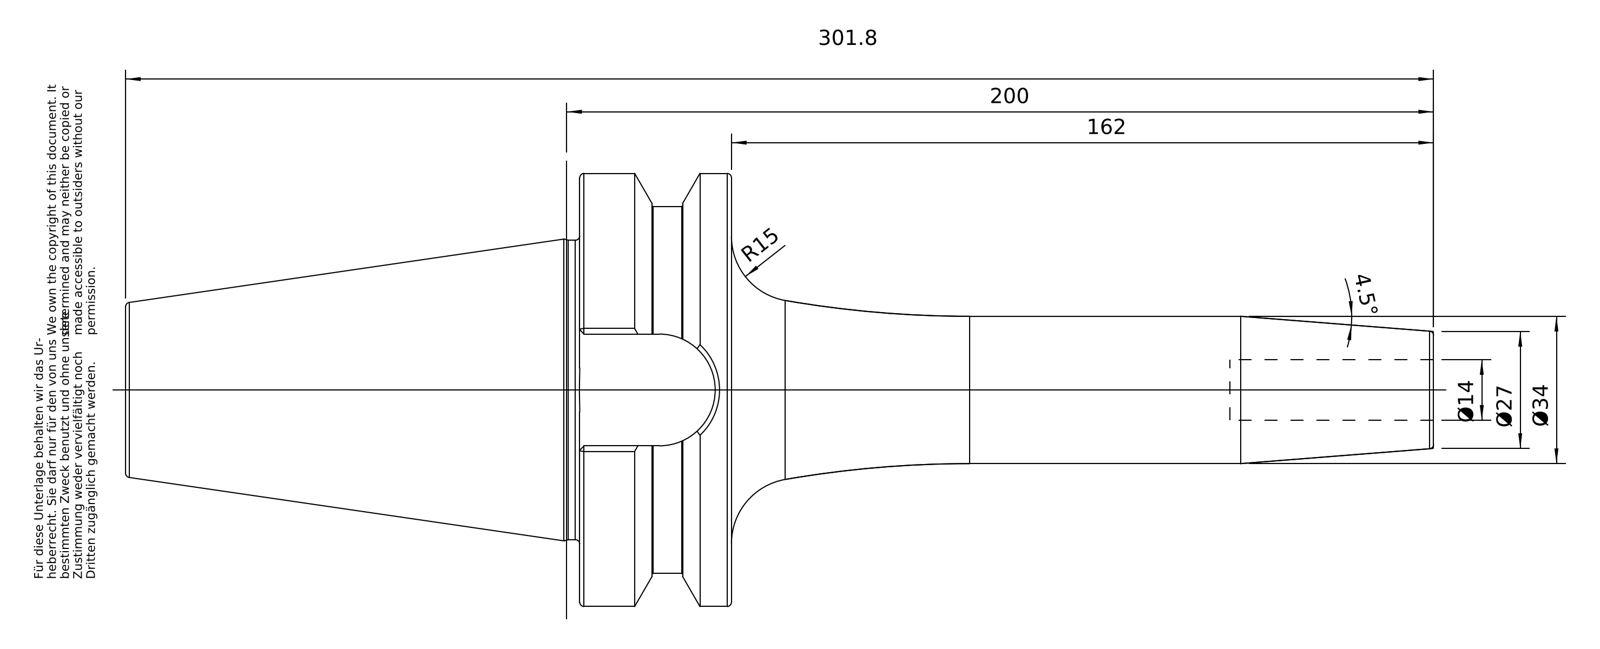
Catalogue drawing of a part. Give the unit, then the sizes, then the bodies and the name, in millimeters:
Units: millimetres
Overall size (bounding box): 301.8 × 99.97 × 99.97
Round holes (diameter × count): ⌀14 ×1, ⌀20.75 ×1, ⌀25.02 ×1, ⌀25.7 ×1
Round bosses / shafts (diameter × count): ⌀99.97 ×1, ⌀84.75 ×1, ⌀69.15 ×1, ⌀34 ×1, ⌀24.01 ×1
Partial cylindrical surfaces — rounded edges, fillets, slot ends (radius × count): R12.9 ×1
Main face-to-face distances: 35, 70.4, 104.8, 139.8, 25.8, 301.8, 197, 162, 254.8, 150
Volume: 618 212 mm³ · Surface area: 69 862 mm²
Bodies: 1 solid, 98 faces (26 planar, 22 cylindrical, 50 other)
Part name (STEP PRODUCT): 50-646-14
STEP written by: PRO/ENGINEER BY PARAMETRIC TECHNOLOGY CORPORATION, 2010430 (CONFIG_CONTROL_DESIGN)
